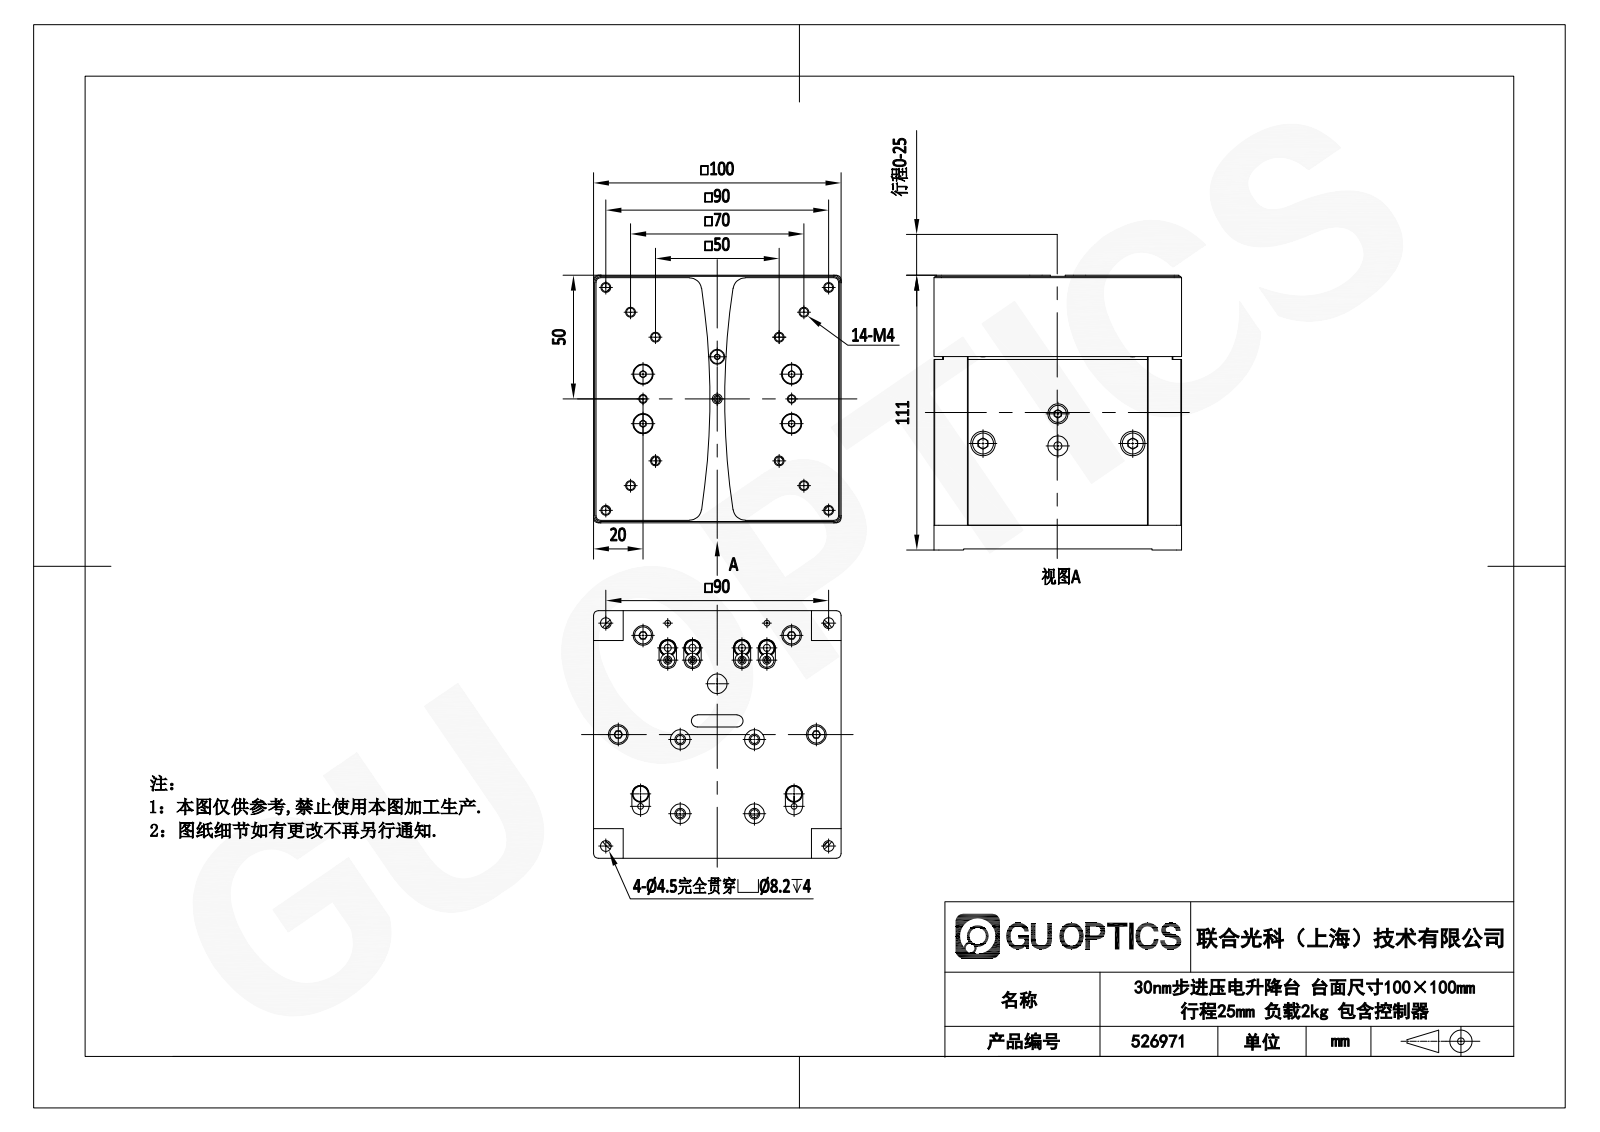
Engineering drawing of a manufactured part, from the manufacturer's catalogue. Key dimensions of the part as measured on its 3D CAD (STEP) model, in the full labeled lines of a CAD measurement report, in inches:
Part name (STEP PRODUCT): hexagon socket button head screws gb_GB_SOCKET_TYPE7 M3X6-S; socket csink head cap screw 10642_din_EN ISO 10642 - M3 x 8 - 8N; hexagon socket head cap screws gb_GB_FASTENER_SCREWS_HSHCS M5X20-N; hexagon socket head cap screws gb_GB_FASTENER_SCREWS_HSHCS M5X16-N (+8 more)
STEP written by: SolidWorks 2020 (CONFIG_CONTROL_DESIGN)
Units: inches
Bodies: 47 solids, 2331 faces (927 planar, 724 cylindrical, 680 other)
Overall size (bounding box): 4.37 × 3.937 × 3.937
Volume: 65.23 in³ · Surface area: 324.8 in²
Round holes (diameter × count): ⌀0.315 ×29, ⌀0.13 ×28, ⌀0.177 ×22, ⌀0.098 ×13, ⌀0.118 ×13, ⌀0.169 ×8, ⌀0.24 ×7, ⌀0.217 ×6, ⌀0.244 ×6, ⌀0.256 ×6, ⌀0.323 ×4, ⌀0.325 ×4
Round bosses / shafts (diameter × count): ⌀0.157 ×22, ⌀0.197 ×13, ⌀0.335 ×11, ⌀0.276 ×11, ⌀0.118 ×5, ⌀0.374 ×4, ⌀0.301 ×4, ⌀0.236 ×4
Partial cylindrical surfaces — rounded edges, fillets, slot ends (radius × count): R0.059 ×20, R0.118 ×16, R0.079 ×12, R0.138 ×12, R0.039 ×9, R0.197 ×8, R0.394 ×4, R0.098 ×2
Main face-to-face distances: 3.937, 3.681, 1.87, 0.02, 2.323, 3.819, 0.374, 0.118, 4.35, 3.976
Hole centre spacings: 0.44, 1.181, 1.575, 3.543, 0.197, 0.394, 0.984, 1.587
